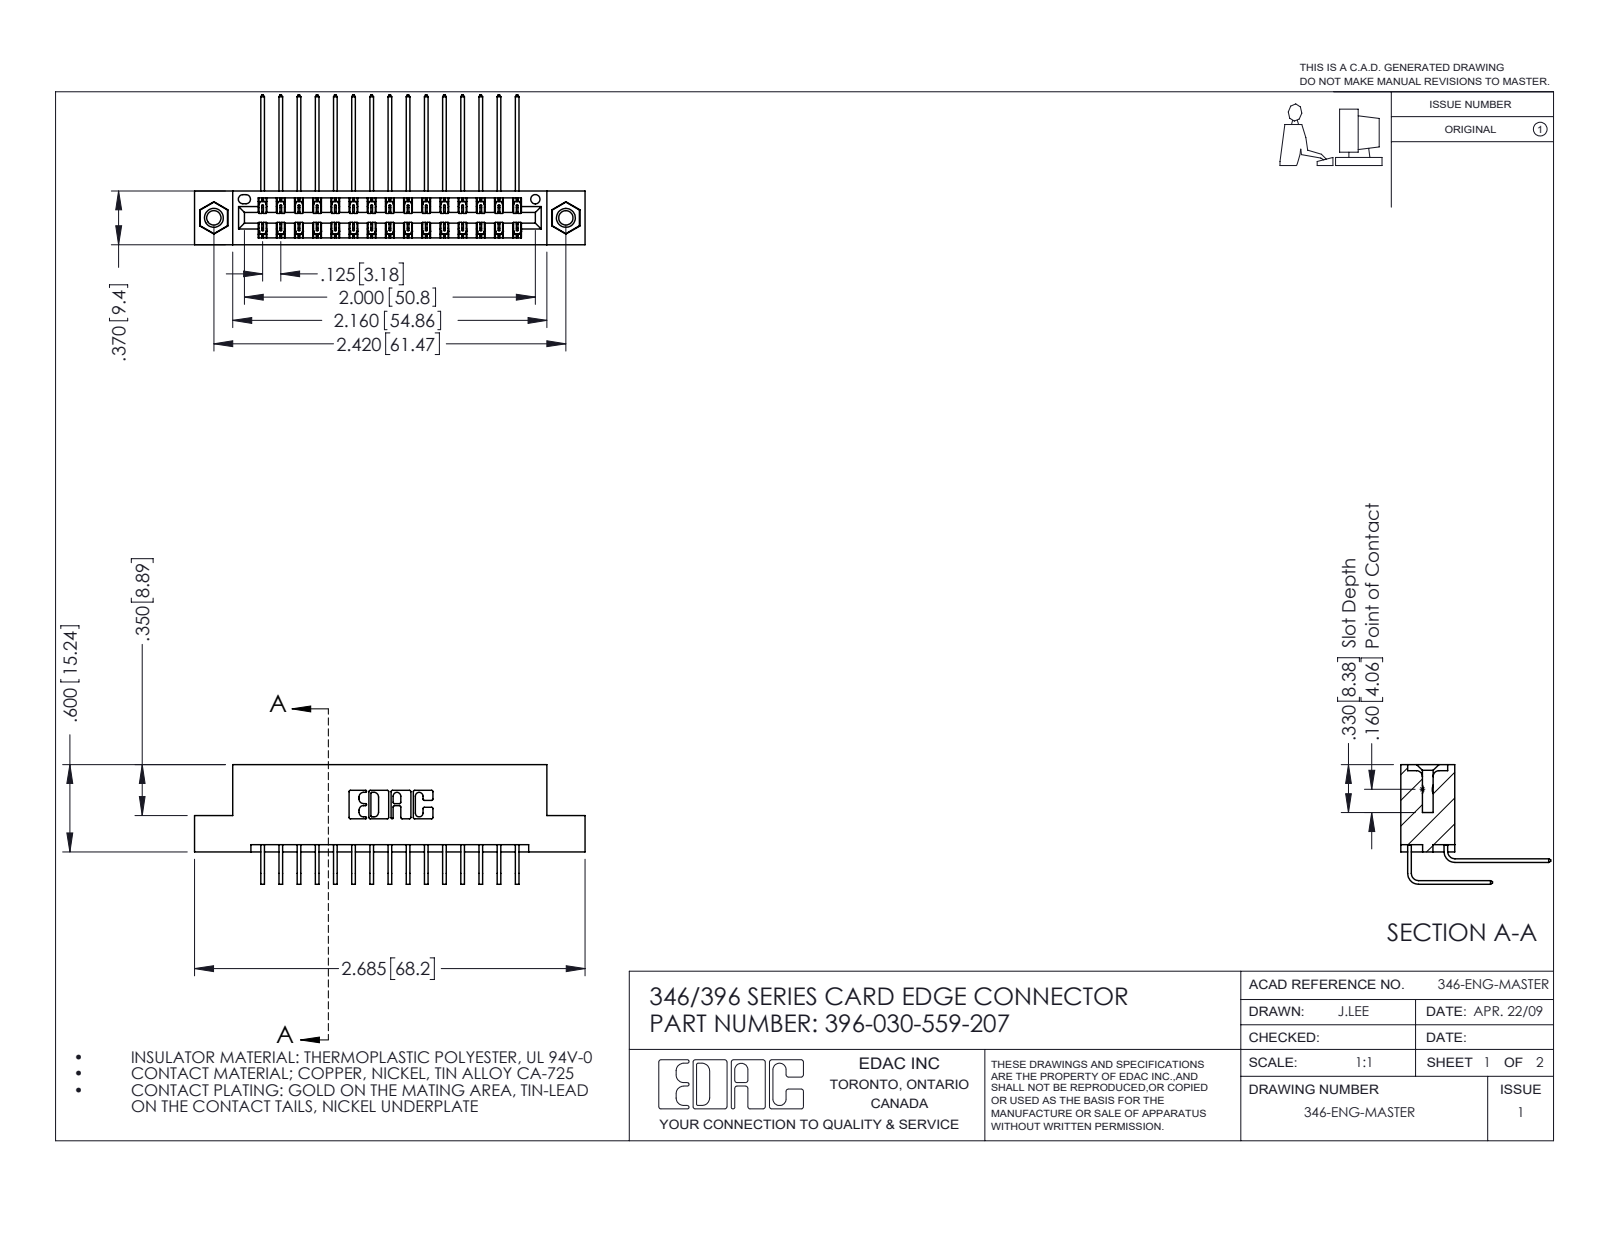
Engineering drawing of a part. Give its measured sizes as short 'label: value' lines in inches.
name: 346 Part_Flush Mounting Lugs - 0.156 Dia-TI; 345-292-001_558 559 Tail - 1; 345-292-001_559 Tail - 2; 396-030-559-207 (+1 more)
written by: SolidWorks 2016 (CONFIG_CONTROL_DESIGN)
unit: in
bodies: 33 solids, 1802 faces (1218 planar, 568 cylindrical, 16 other)
size: 2.685 × 1.03 × 0.823
volume: 0.403 in³; area: 14.74 in²
holes: 2× ⌀0.098, 2× ⌀0.125, 2× ⌀0.156, 1× ⌀0.064
bosses: 2× ⌀0.155
rounds: 45× R0.006, 22× R0.01, 6× R0.007, 6× R0.031, 3× R0.026, 2× R0.014, 2× R0.022, 2× R0.024
face distances: 0.048, 0.322, 0.25, 0.025, 0.37, 0.072, 0.298, 0.275, 0.148, 0.222
hole spacings: 0.246, 2.213, 2.42
